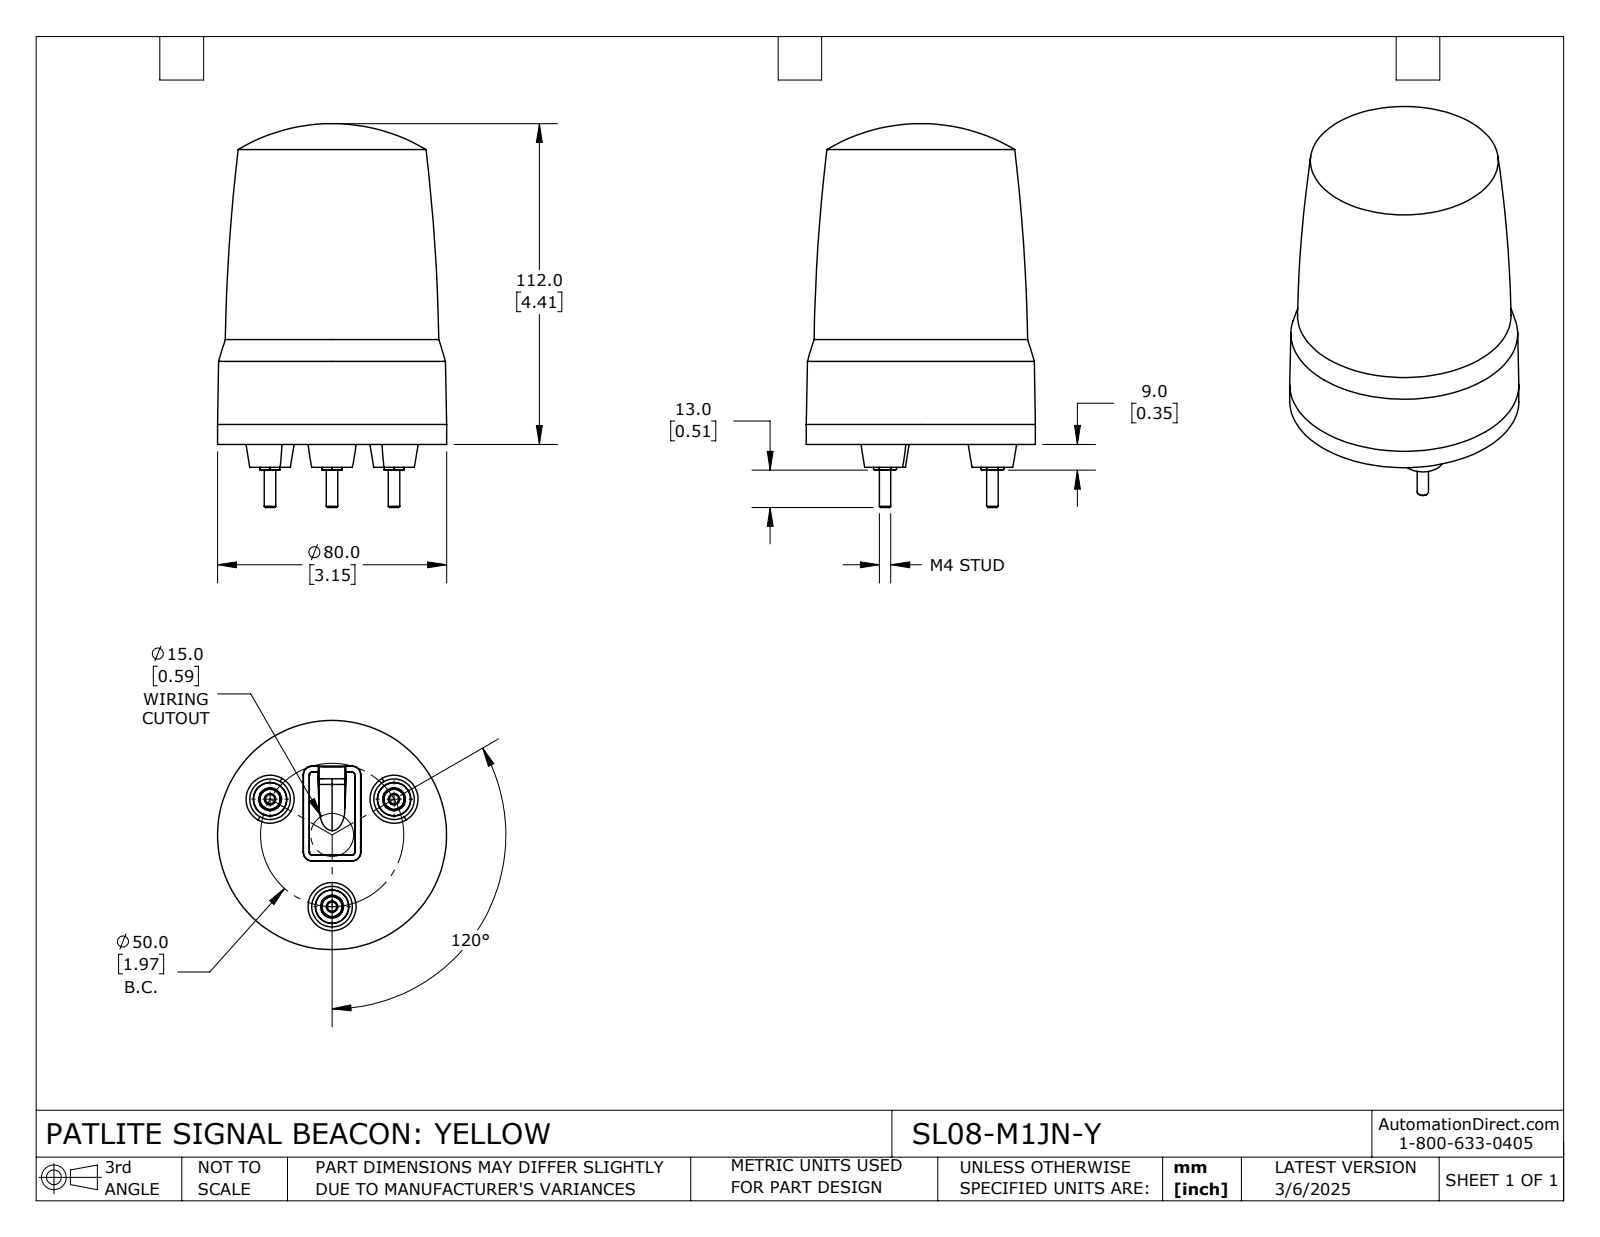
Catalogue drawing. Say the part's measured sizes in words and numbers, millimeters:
The part is named "SL08-M1JN-Y". Its 3-D file was written by "SolidWorks 2024 (CONFIG_CONTROL_DESIGN)". It is 1 solid with 138 faces: 47 planar, 14 cylindrical and 77 other. Overall it measures 134 by 80 by 80 millimeters. Its volume is 463 225 cubic millimeters and its surface area 35 408 square millimeters. Round bosses or shafts: 3 of diameter 8, 3 of diameter 4, 1 of diameter 80. The main face-to-face distances are 0.85, 2.45, 1.6, 5.3, 6.15, 7.75, 2.7, 8, 8.85, 10.45.
